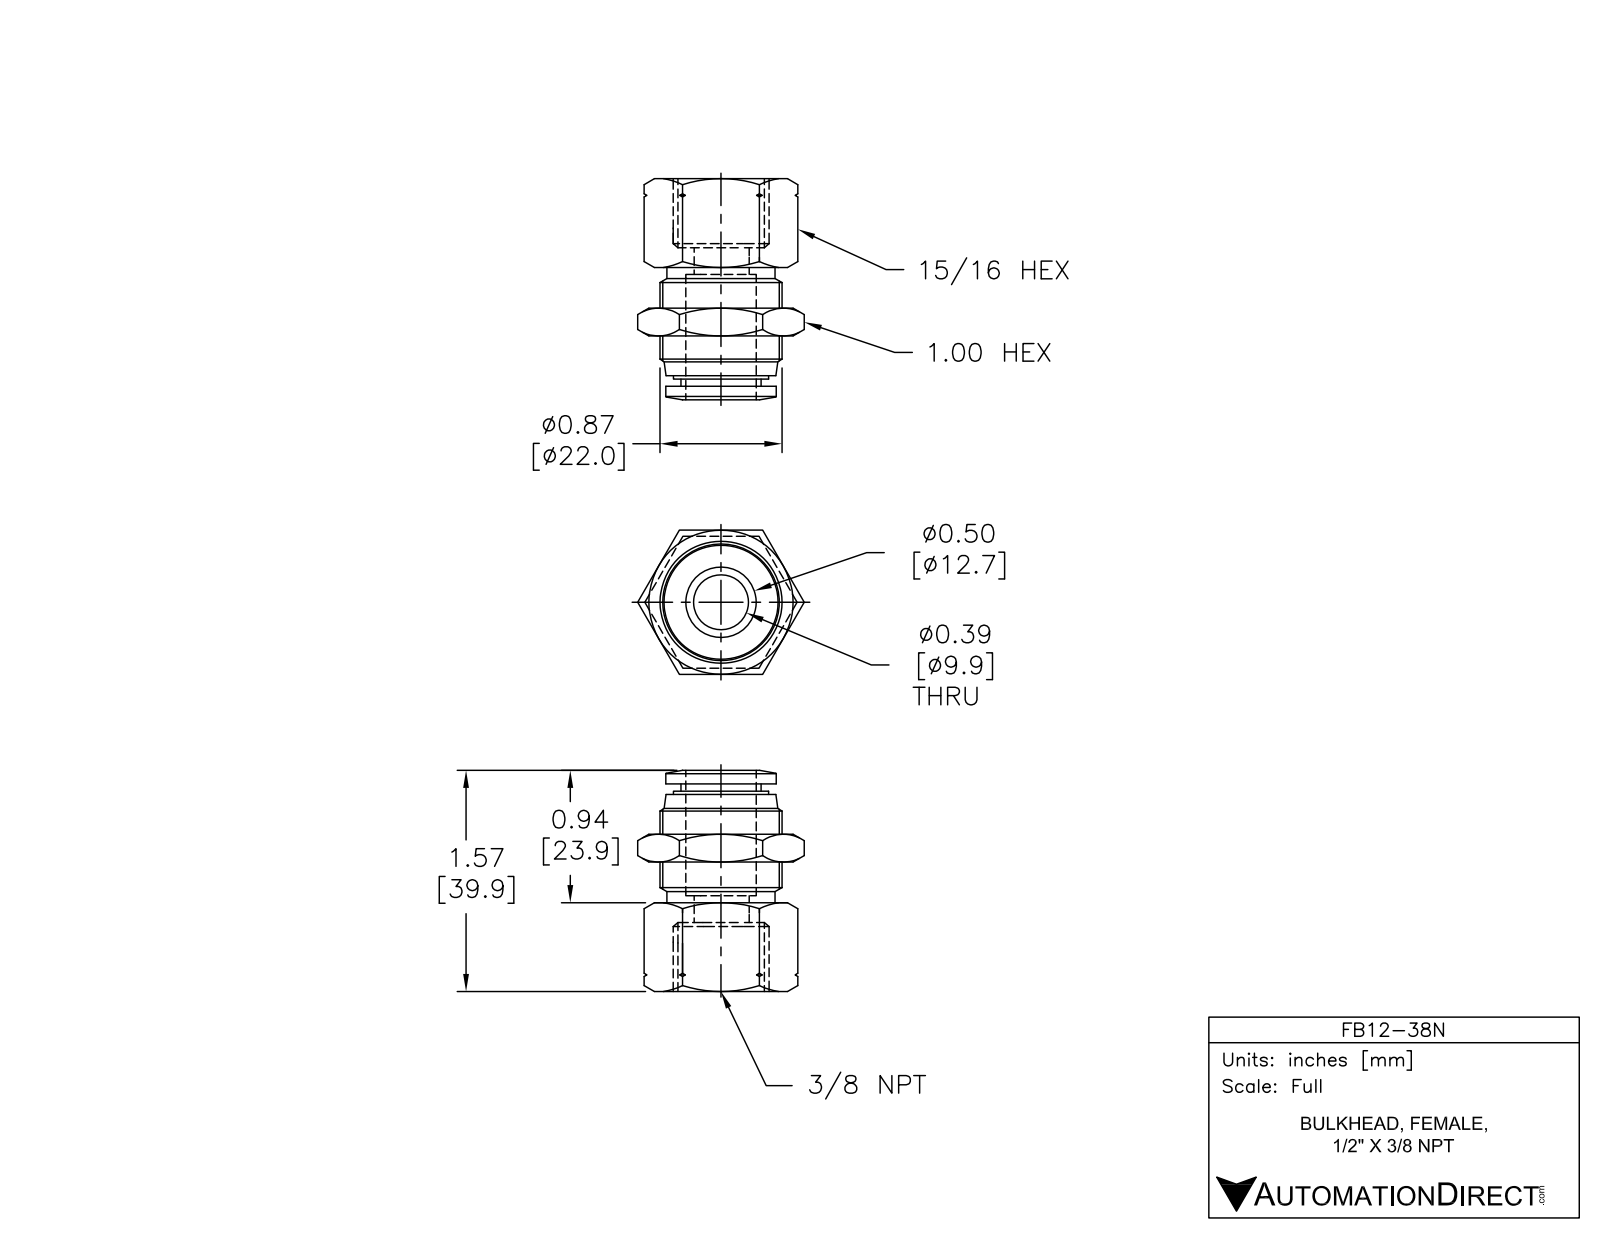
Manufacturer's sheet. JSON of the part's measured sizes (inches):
{"part_name": "FB12-38N", "step_written_by": "SolidWorks 2015 (AUTOMOTIVE_DESIGN)", "units": "inches", "bodies": {"solids": 1, "faces": 95, "planar": 21, "cylindrical": 16, "other": 58}, "overall_size": [1.569, 1.182, 1.024], "volume_in3": 0.66, "surface_area_in2": 9.68, "round_holes": [[0.394, 1], [0.51, 1]], "round_bosses_or_shafts": [[0.866, 1], [0.783, 1], [0.709, 1], [0.675, 1], [0.569, 1]], "face_to_face_distances": [0.945, 0.039, 0.984, 0.63, 1.024, 0.919, 0.289, 1.115, 0.485, 0.197]}
